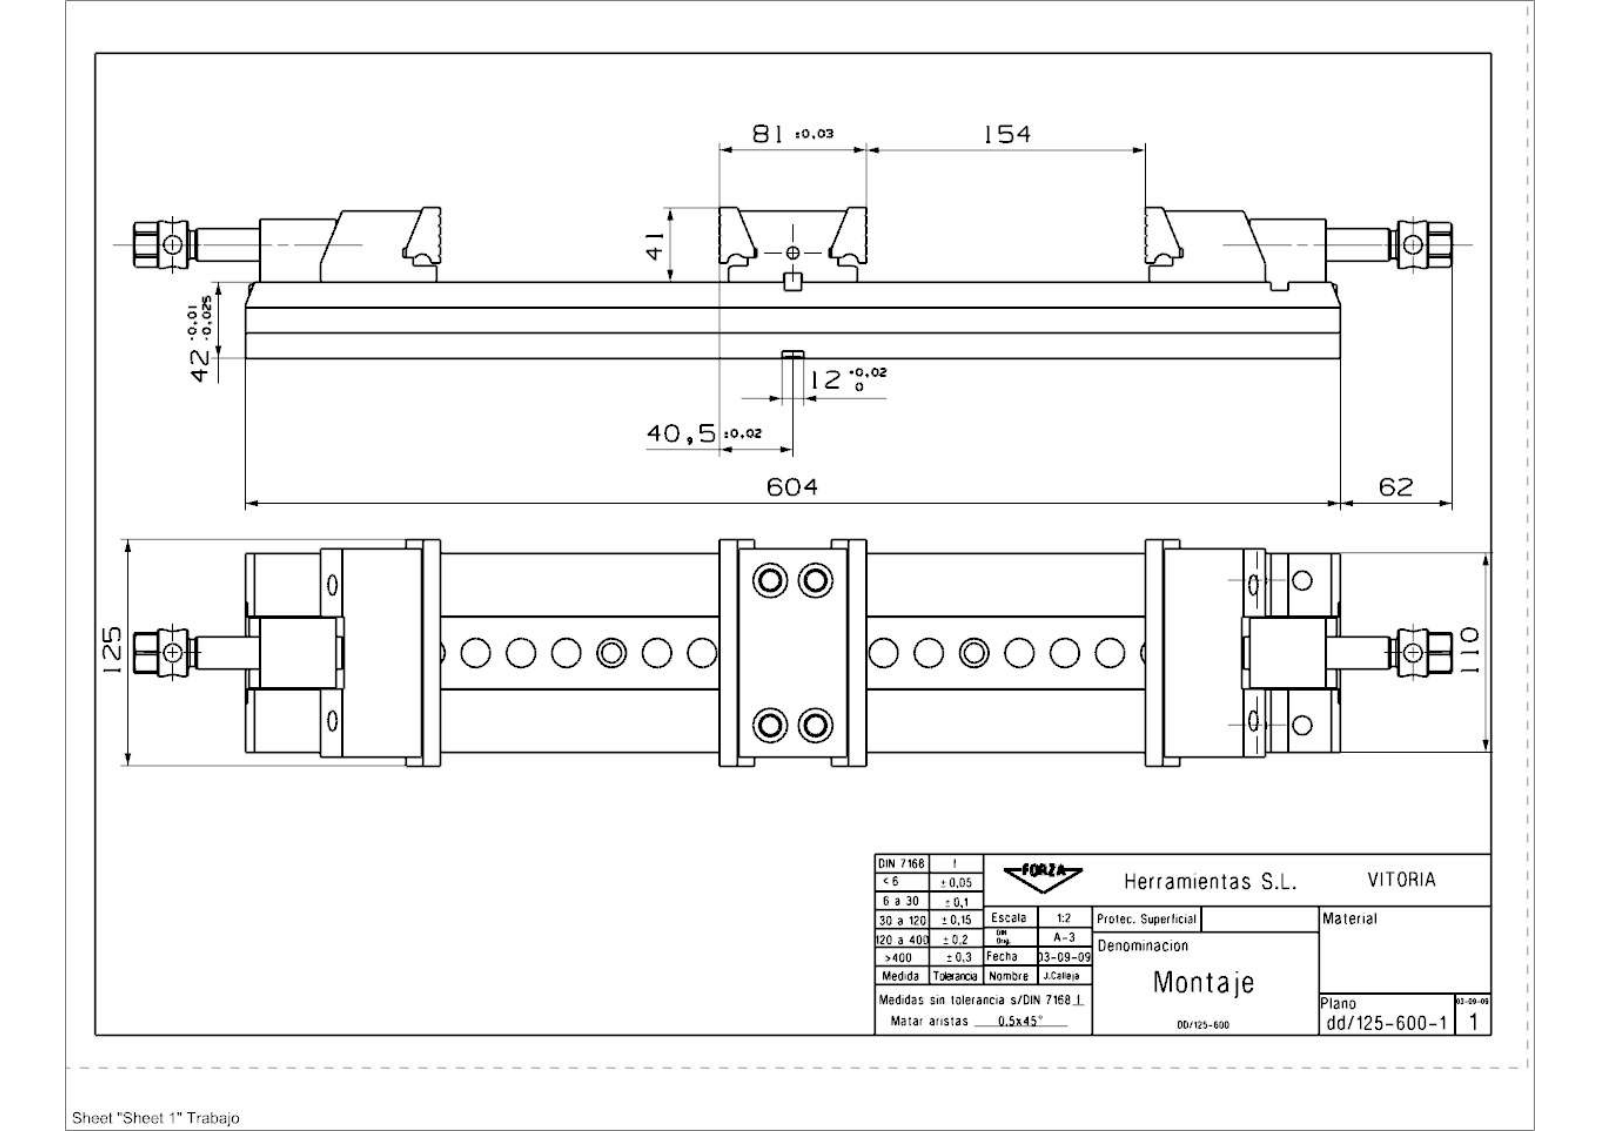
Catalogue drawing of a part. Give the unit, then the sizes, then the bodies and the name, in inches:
Units: inches
Overall size (bounding box): 28.63 × 4.921 × 3.268
Round holes (diameter × count): ⌀0.433 ×9, ⌀0.417 ×8, ⌀0.63 ×5, ⌀0.204 ×4, ⌀0.275 ×4, ⌀0.295 ×4, ⌀0.346 ×4, ⌀0.394 ×4, ⌀0.492 ×4, ⌀0.669 ×4, ⌀0.748 ×4, ⌀0.167 ×2
Round bosses / shafts (diameter × count): ⌀1.024 ×1, ⌀0.698 ×1, ⌀0.591 ×1, ⌀0.571 ×1, ⌀0.413 ×1
Partial cylindrical surfaces — rounded edges, fillets, slot ends (radius × count): R0.012 ×20, R0.63 ×8, R0.236 ×5, R0.157 ×4, R0.197 ×4, R0.394 ×4, R0.063 ×2, R0.118 ×2
Main face-to-face distances: 1.654, 0.197, 1.063, 3.268, 1.535, 0.622, 1.031, 0.551, 1.614, 0.866
Hole centre spacings: 0.138, 0.453, 0.511, 0.795, 0.799, 0.984, 1.65, 1.909
Volume: 182.3 in³ · Surface area: 802.5 in²
Bodies: 19 solids, 774 faces (489 planar, 198 cylindrical, 87 other)
Part name (STEP PRODUCT): DD_125_600_Mordaza_Doble
STEP written by: SIEMENS PLM Software NX 7.5 (AUTOMOTIVE_DESIGN)
